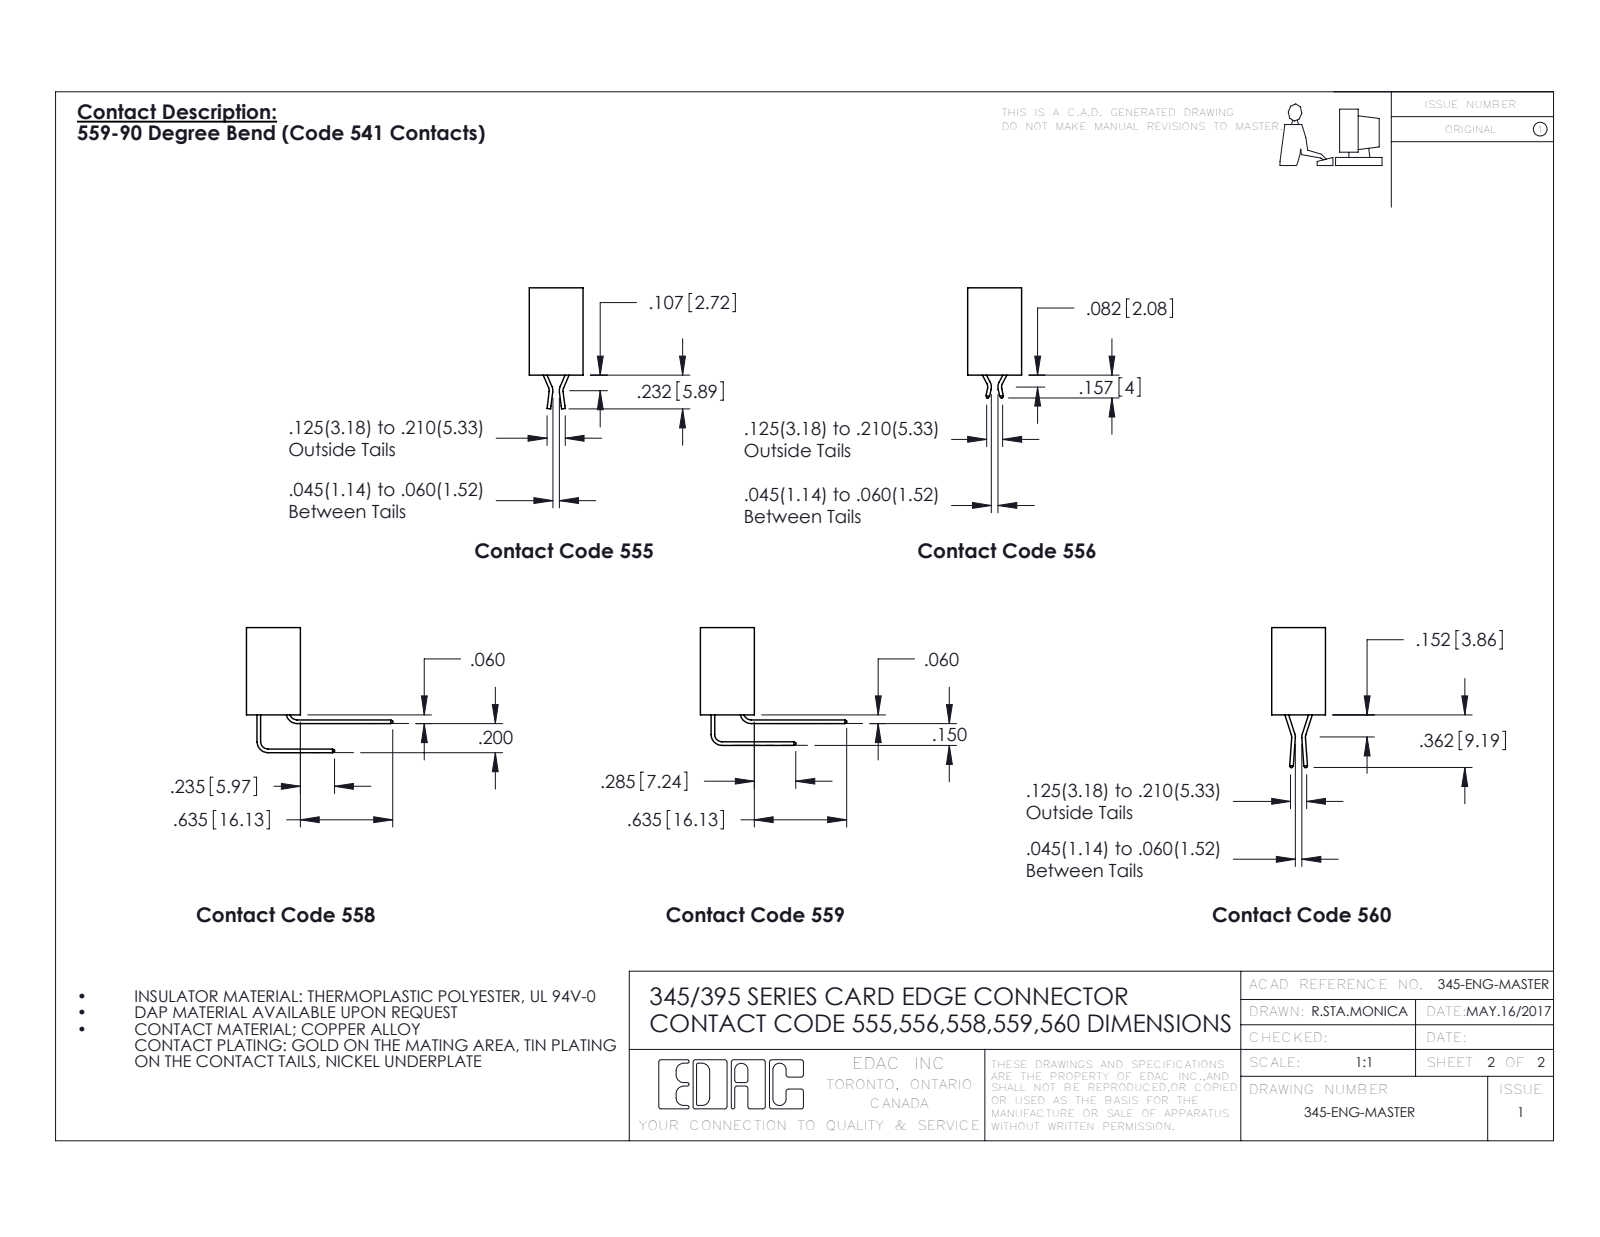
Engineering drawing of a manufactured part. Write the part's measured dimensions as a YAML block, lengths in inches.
part_name: "395-022-555-812; 345 Part_0.170 Offset - Side Mount; 345-292-001_555 Tail"
step_written_by: "SolidWorks 2016 (CONFIG_CONTROL_DESIGN)"
units: inches
bodies: {solids: 23, faces: 1362, planar: 766, cylindrical: 596, other: 0}
overall_size: [1.935, 0.832, 0.37]
volume: 0.265
surface_area: 9.392
round_holes:
  - {diameter: 0.128, count: 2}
  - {diameter: 0.064, count: 1}
partial_cylinders:
  - {radius: 0.016, count: 55}
  - {radius: 0.02, count: 44}
  - {radius: 0.006, count: 33}
  - {radius: 0.01, count: 22}
  - {radius: 0.007, count: 6}
  - {radius: 0.031, count: 6}
  - {radius: 0.026, count: 3}
  - {radius: 0.01, count: 2}
face_to_face_distances: [0.37, 0.298, 0.072, 0.2, 0.025, 0.098, 0.272, 0.1, 0.225, 0.6]
hole_center_spacings: [1.675]
